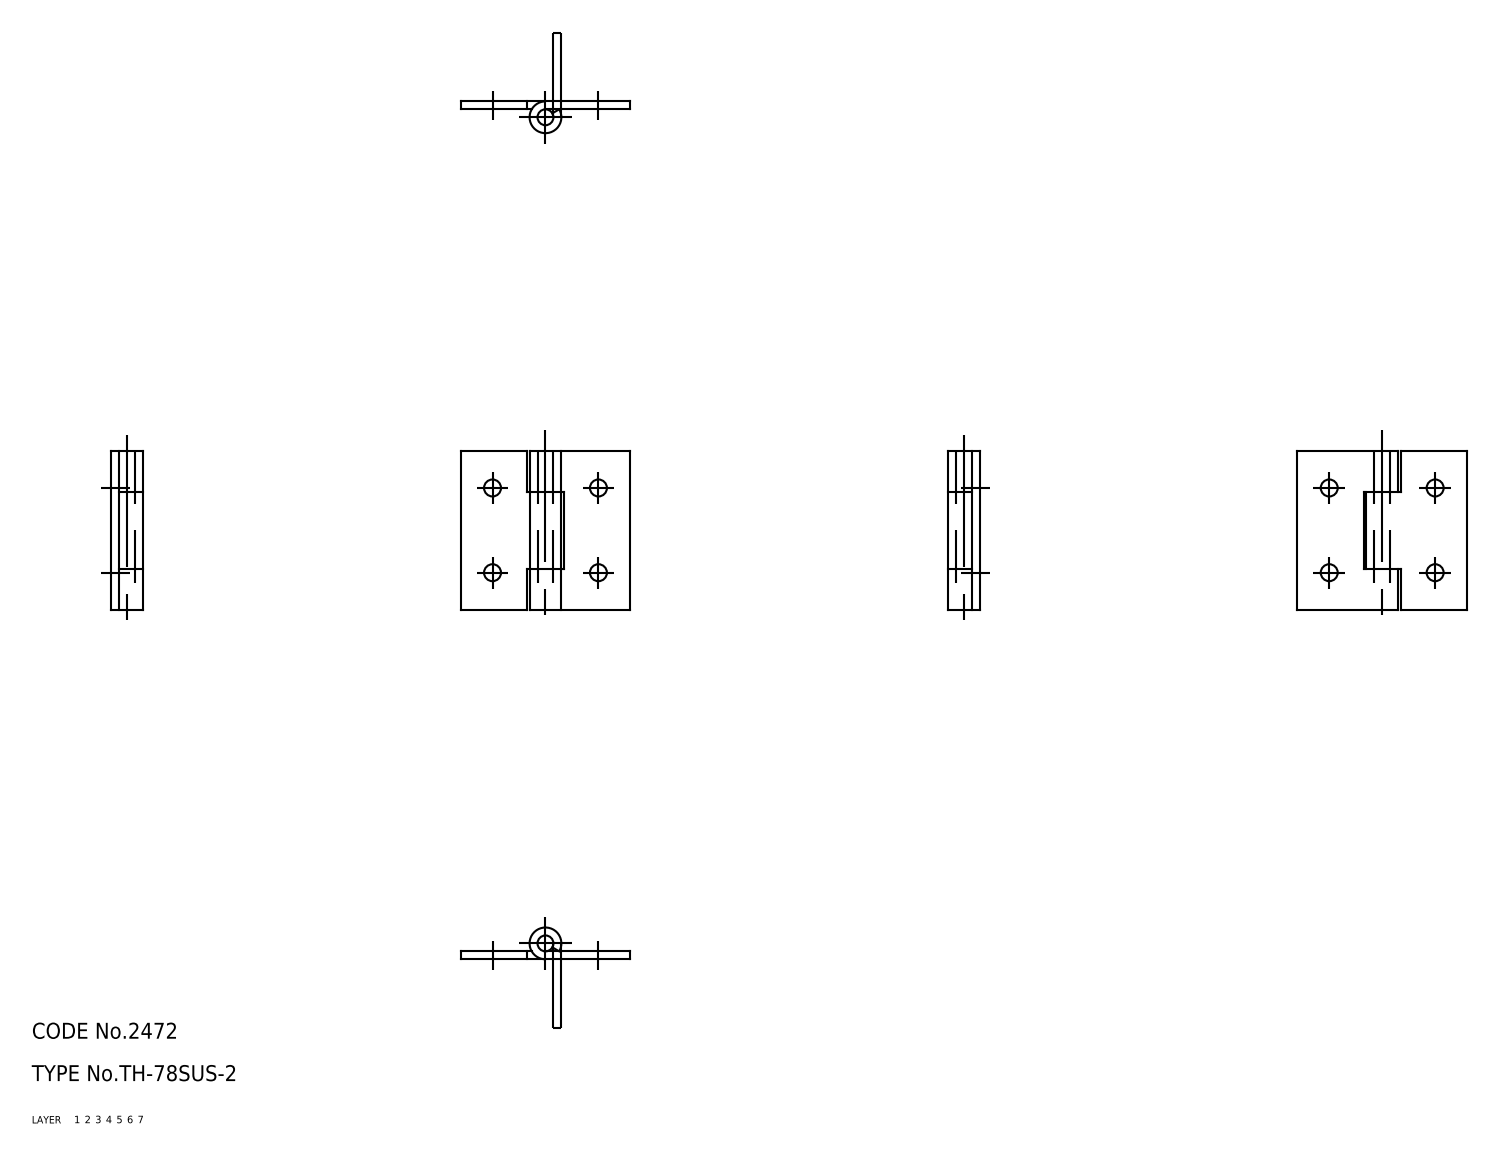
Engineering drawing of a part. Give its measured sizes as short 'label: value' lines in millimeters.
name: hinge piece_B; hinge piece_A; shaft; TH_78SUS_2_17141_36
written by: CADfix (AUTOMOTIVE_DESIGN)
unit: mm
bodies: 3 solids, 38 faces (0 planar, 0 cylindrical, 38 other)
size: 32 × 30 × 6
volume: 1 975 mm³; area: 3 100 mm²
